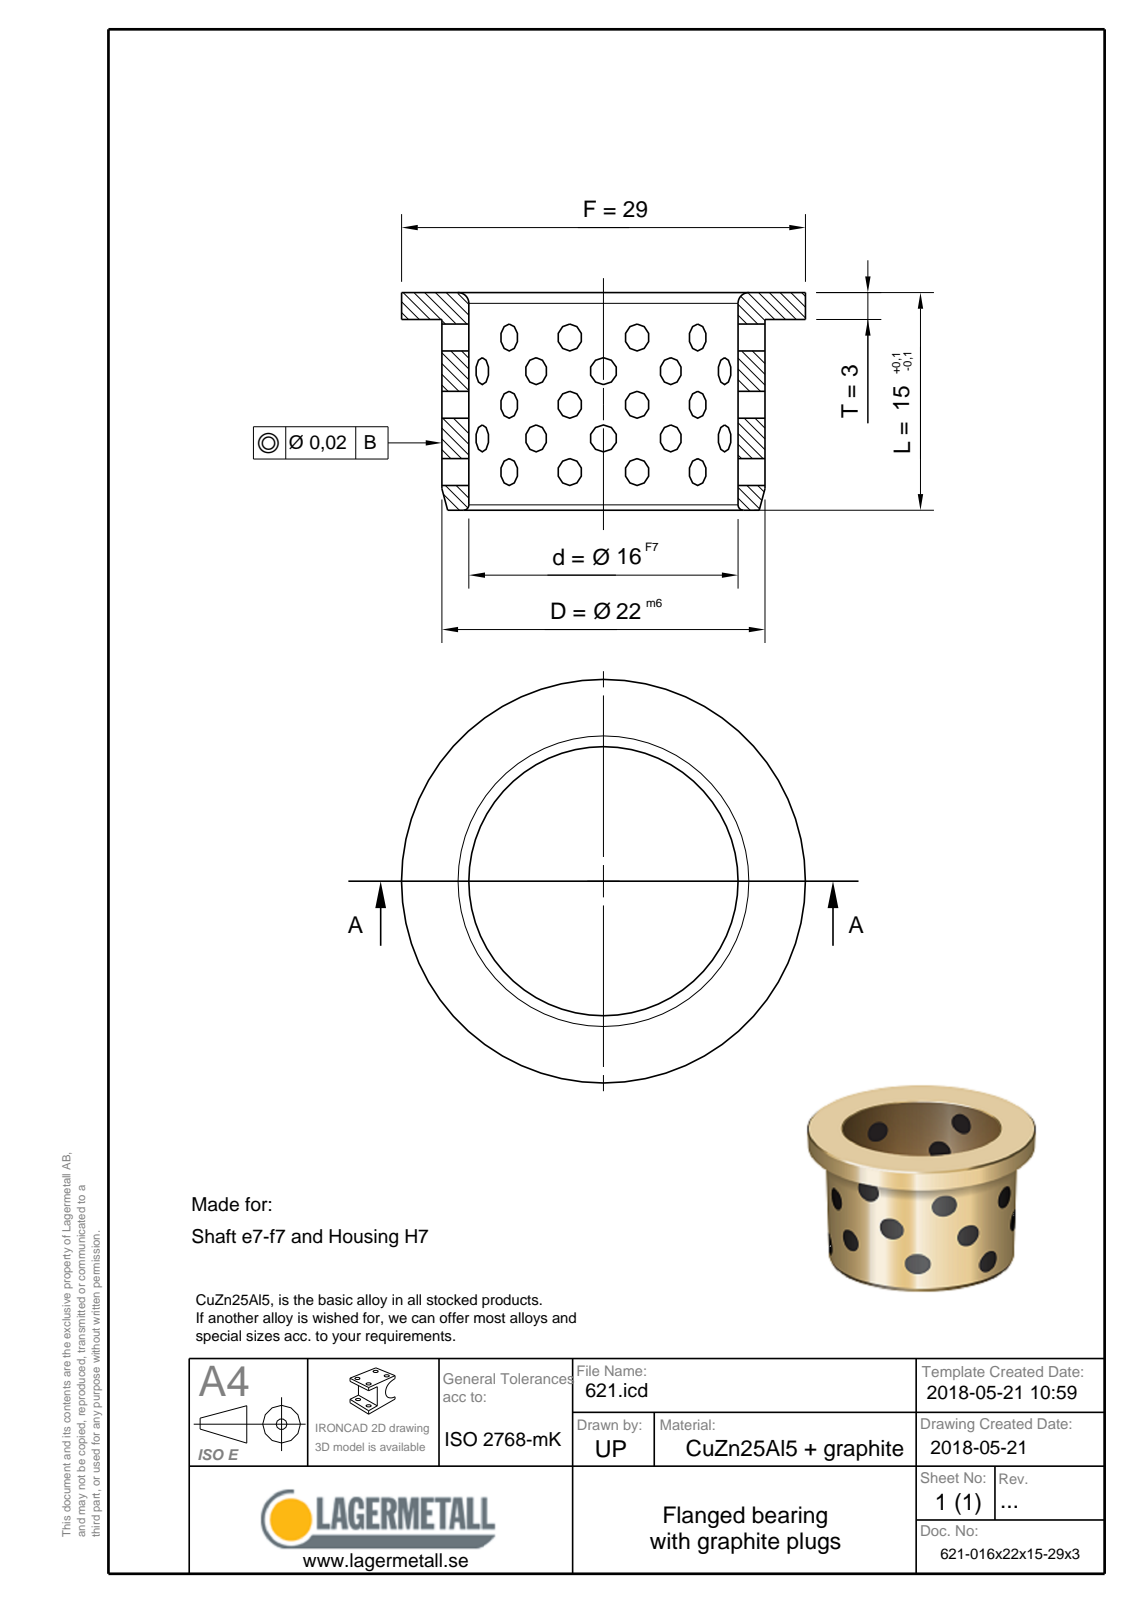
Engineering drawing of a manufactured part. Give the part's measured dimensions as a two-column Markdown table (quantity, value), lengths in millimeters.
| quantity | value |
| --- | --- |
| part name | 621-016x22x15-29x3 |
| STEP written by | Spatial InterOp 3D (CONFIG_CONTROL_DESIGN) |
| units | millimeters |
| bodies | 1 solid, 9 faces (3 planar, 3 cylindrical, 3 other) |
| overall size | 29 × 29 × 15 |
| volume | 3 429 mm³ |
| surface area | 2 668 mm² |
| round holes (diameter × count) | 16 × 1 |
| round bosses / shafts (diameter × count) | 29 × 1, 22 × 1 |
| main face-to-face distances | 3, 12, 15 |
